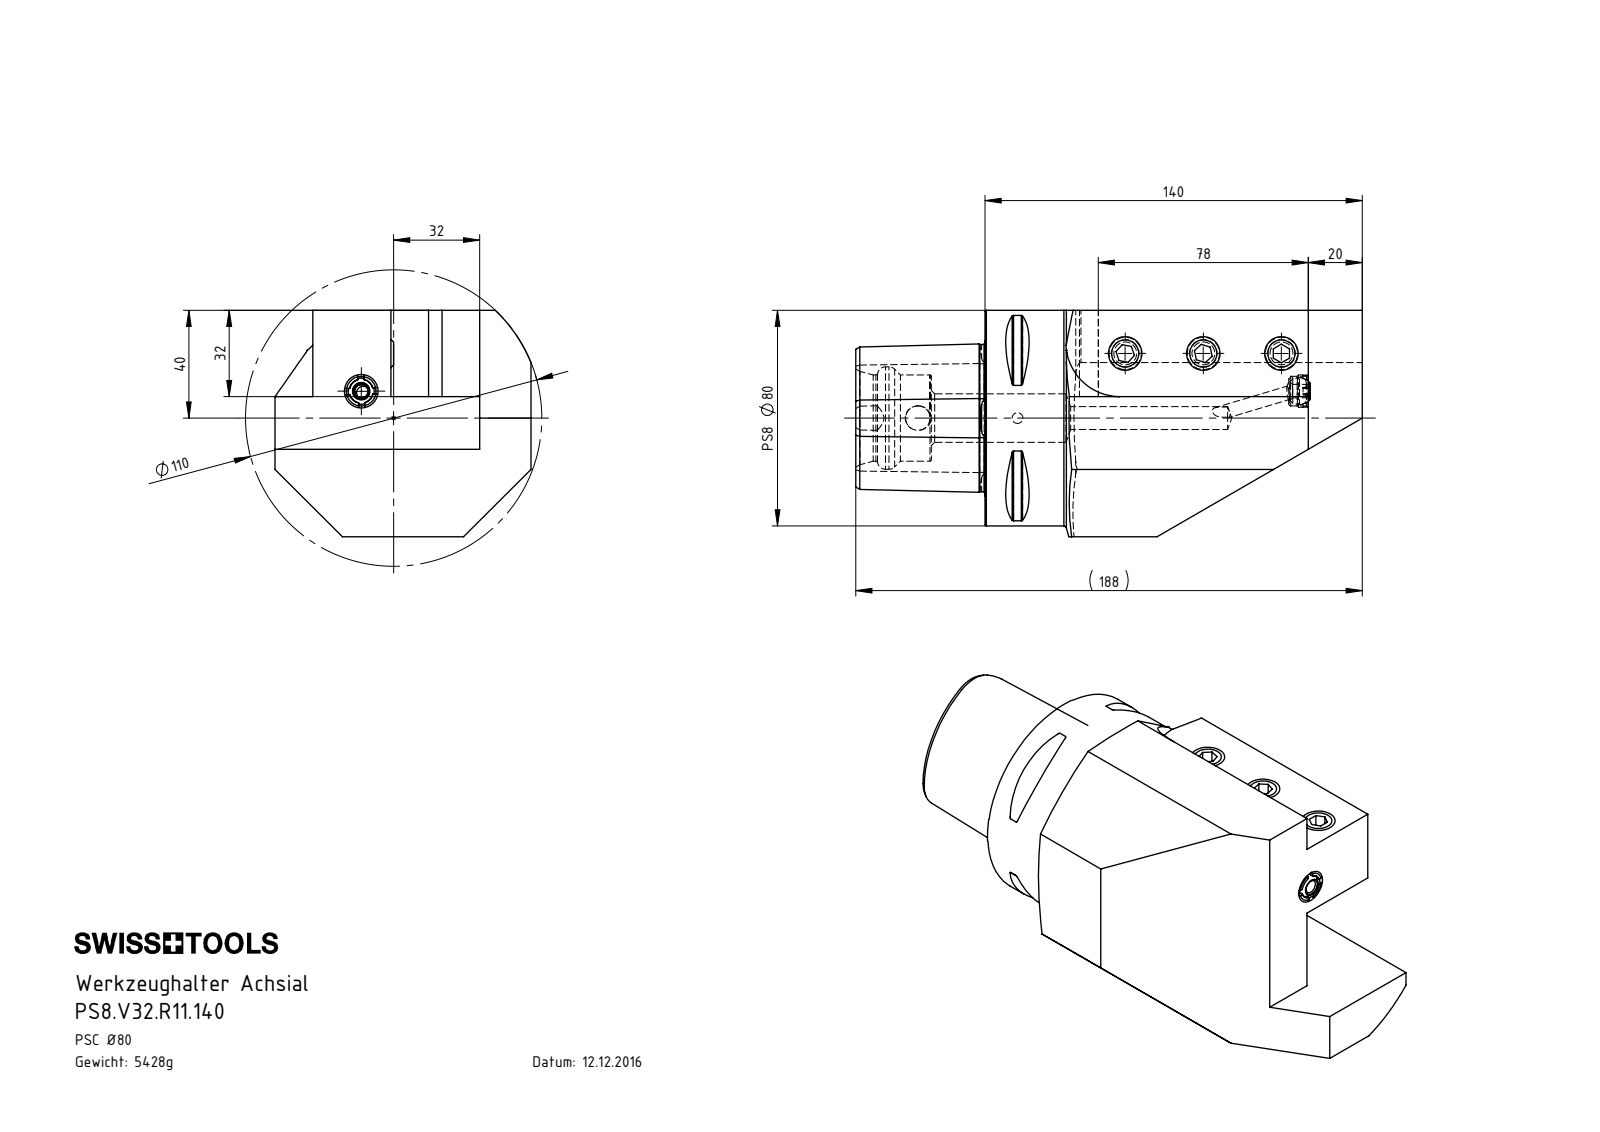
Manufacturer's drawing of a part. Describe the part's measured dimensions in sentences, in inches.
The part is named "KU1-U12.002.010_A; DIN 3771 - 8x1.5; KU1-U12.002.010; PS8-V32.R11.140 (+3 more)". Its 3-D file was written by "SolidWorks 2017 (AUTOMOTIVE_DESIGN)". It is 7 solids with 269 faces: 79 planar, 58 cylindrical and 132 other. Overall it measures 7.402 by 3.74 by 3.307 inches. Its volume is 42.2 cubic inches and its surface area 122 square inches. Round holes: 3 of diameter 0.402, 2 of diameter 0.197, 1 of diameter 0.157, 1 of diameter 0.335, 1 of diameter 0.358, 1 of diameter 0.394, 1 of diameter 0.433, 1 of diameter 0.709, 1 of diameter 1.26, 1 of diameter 1.496. Round bosses or shafts: 4 of diameter 0.472, 1 of diameter 3.15. Partial cylindrical surfaces (rounded edges, fillets, slot ends): 8 of radius 0.02, 2 of radius 0.276, 1 of radius 0.173, 1 of radius 0.236, 1 of radius 0.472, 1 of radius 0.787, 1 of radius 2.165. The main face-to-face distances are 2.047, 1.26, 0.748, 2.441, 3.189, 2.992, 3.74, 0.551, 1.299, 1.142. The hole center spacings are 1.142, 0.615, 1.457, 1.837, 2.283, 2.876, 3.175, 3.972.
